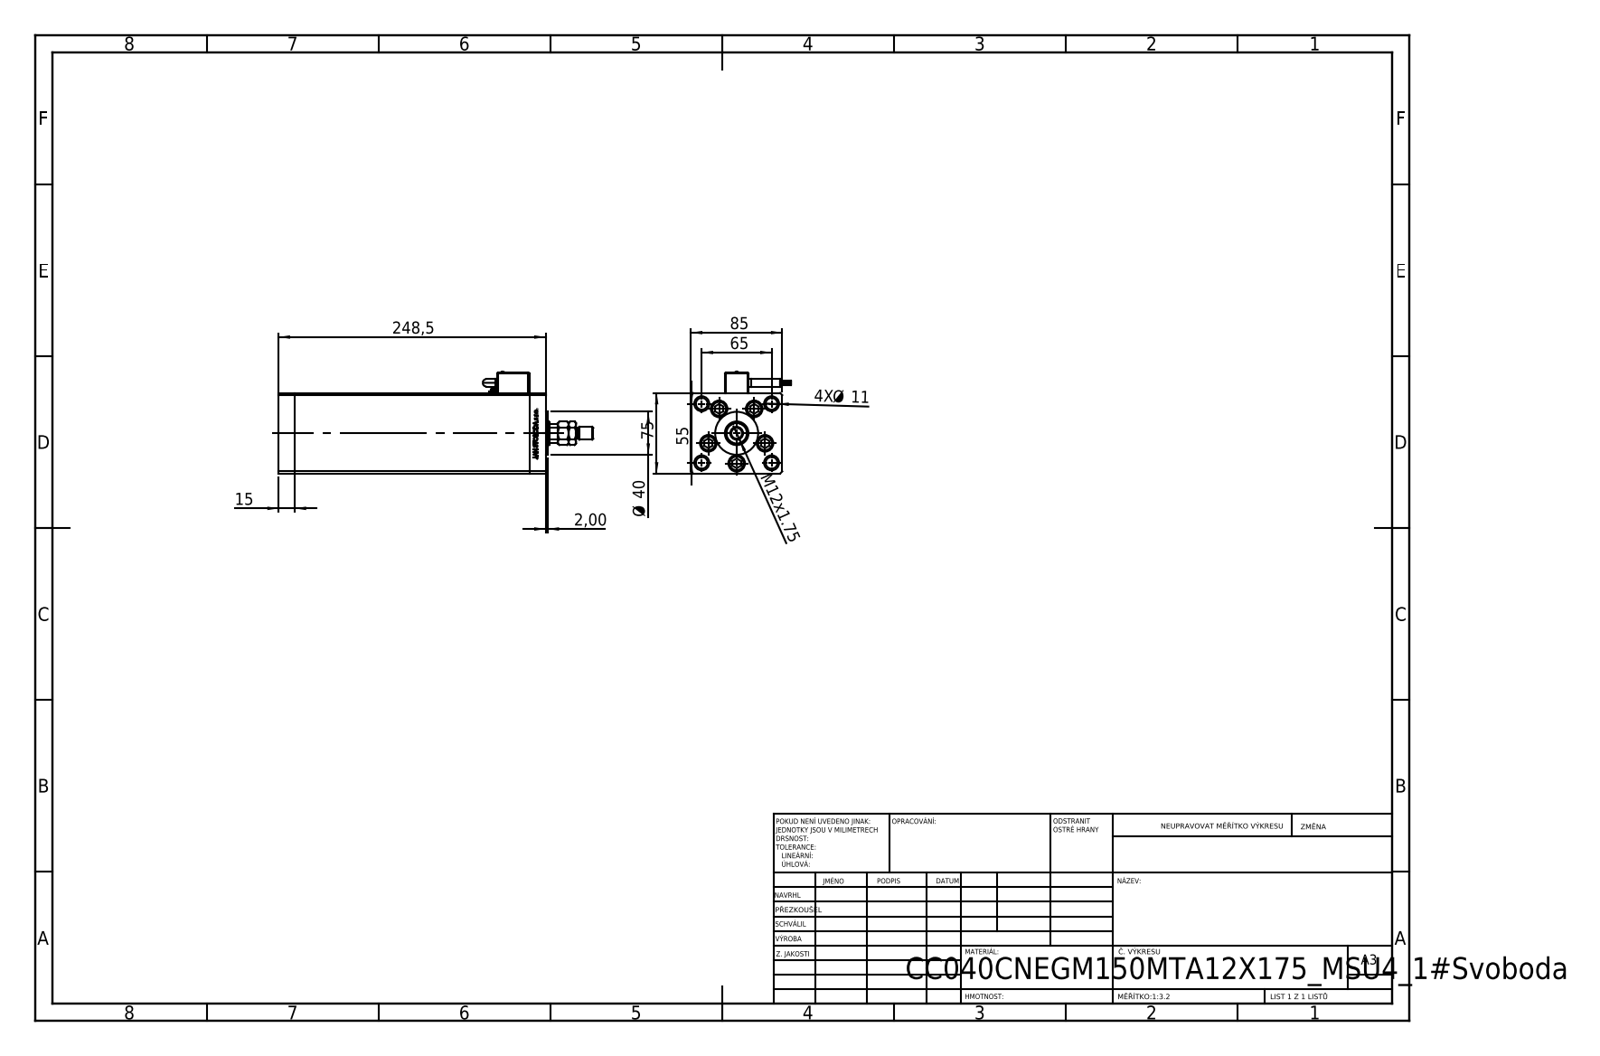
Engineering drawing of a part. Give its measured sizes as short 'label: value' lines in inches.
name: V220C BACK_C; Magnetic_Switch_MSU4; ALLEN BOLT; V220C_VC_C (+3 more)
written by: SolidWorks 2019 (CONFIG_CONTROL_DESIGN)
unit: in
bodies: 15 solids, 1314 faces (596 planar, 208 cylindrical, 510 other)
size: 11.535 × 3.744 × 3.673
volume: 81.77 in³; area: 352.7 in²
holes: 9× ⌀0.433, 5× ⌀0.61, 4× ⌀0.394, 4× ⌀0.551, 1× ⌀0.142, 1× ⌀0.197, 1× ⌀0.276, 1× ⌀0.531, 1× ⌀0.571, 1× ⌀0.866
bosses: 5× ⌀0.315, 4× ⌀0.571, 4× ⌀0.033, 2× ⌀0.276, 1× ⌀1.575, 1× ⌀0.472, 1× ⌀0.394, 1× ⌀0.236
rounds: 14× R0.039, 2× R0.037, 2× R0.157, 1× R0.413
face distances: 3.346, 2.953, 0.591, 8.602, 9.193, 0.413, 2.697, 9.783, 1.348, 0.256
hole spacings: 1.102, 1.676, 0.664, 0.755, 1.273, 1.28, 1.324, 1.47
